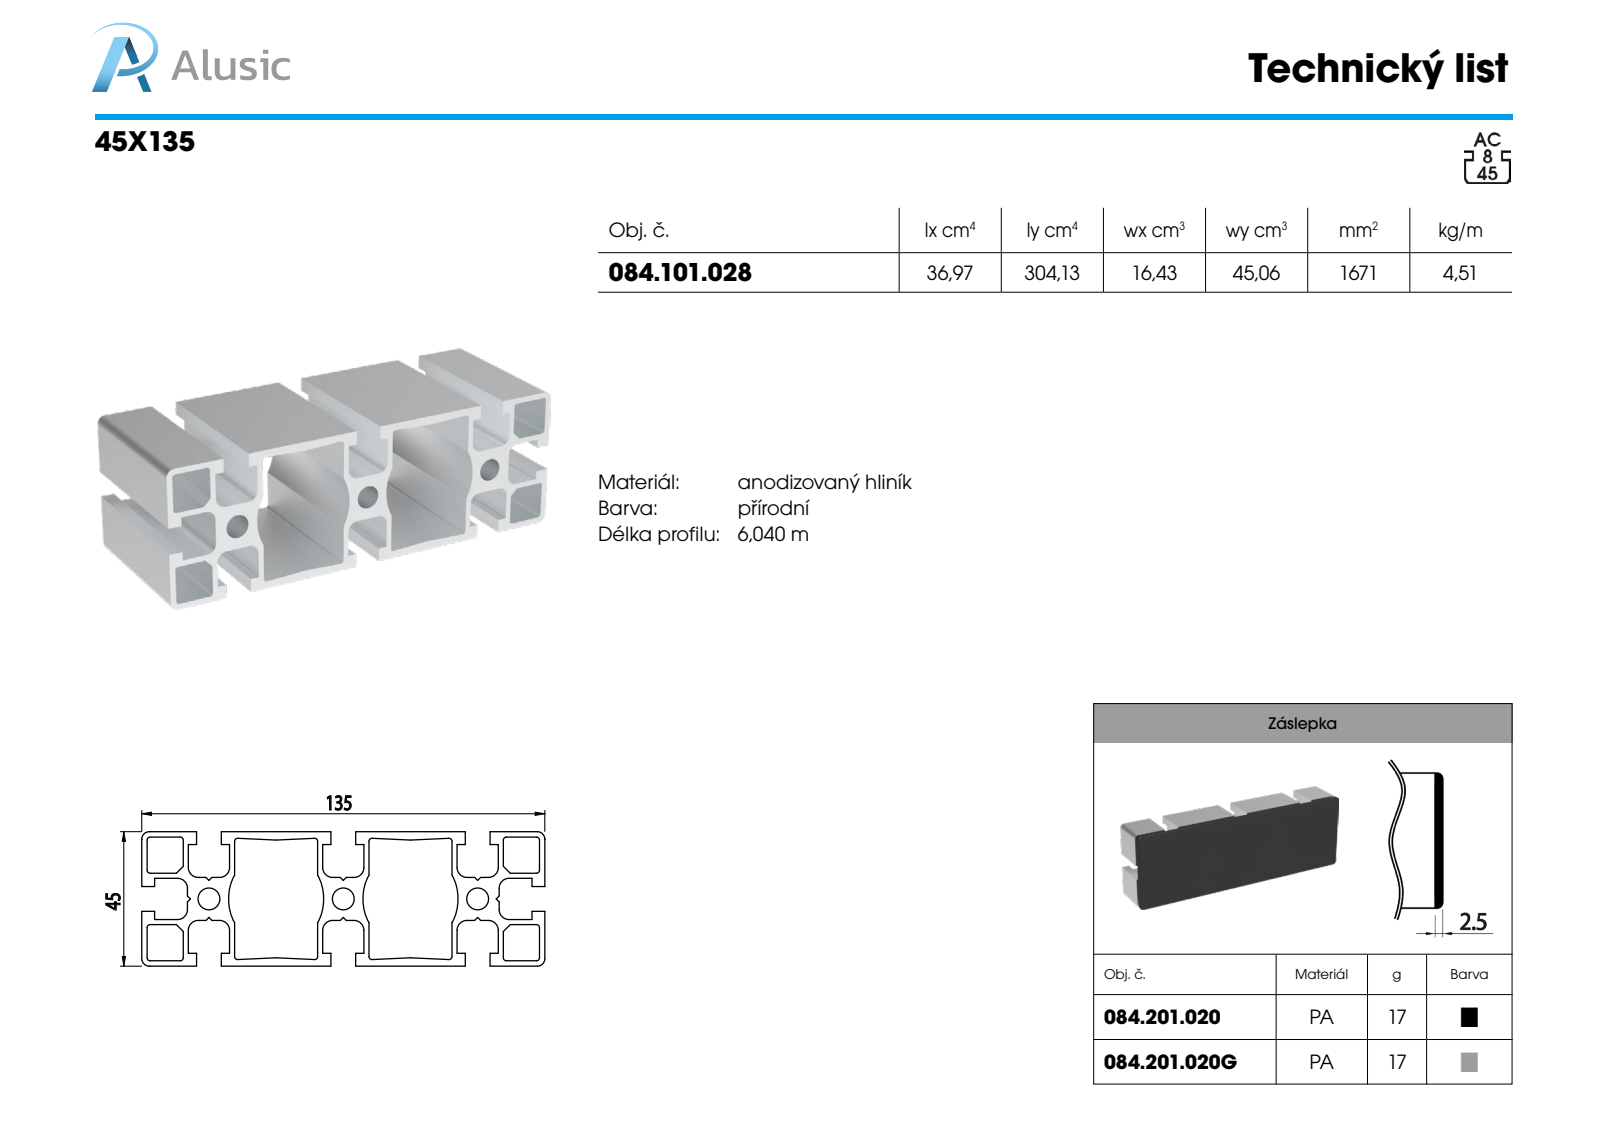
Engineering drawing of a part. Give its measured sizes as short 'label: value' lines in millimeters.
name: 084.101.028
written by: SolidWorks 2018 (AUTOMOTIVE_DESIGN)
unit: mm
bodies: 1 solid, 160 faces (106 planar, 54 cylindrical, 0 other)
size: 135 × 100 × 45
volume: 159 365 mm³; area: 122 428 mm²
holes: 3× ⌀7.3
rounds: 20× R1, 16× R3, 4× R2.5, 4× R16.5
face distances: 45, 13.8, 1.7, 15.5, 1.8, 31.1, 29.3, 17.2, 13.9, 12.1
hole spacings: 45, 90
